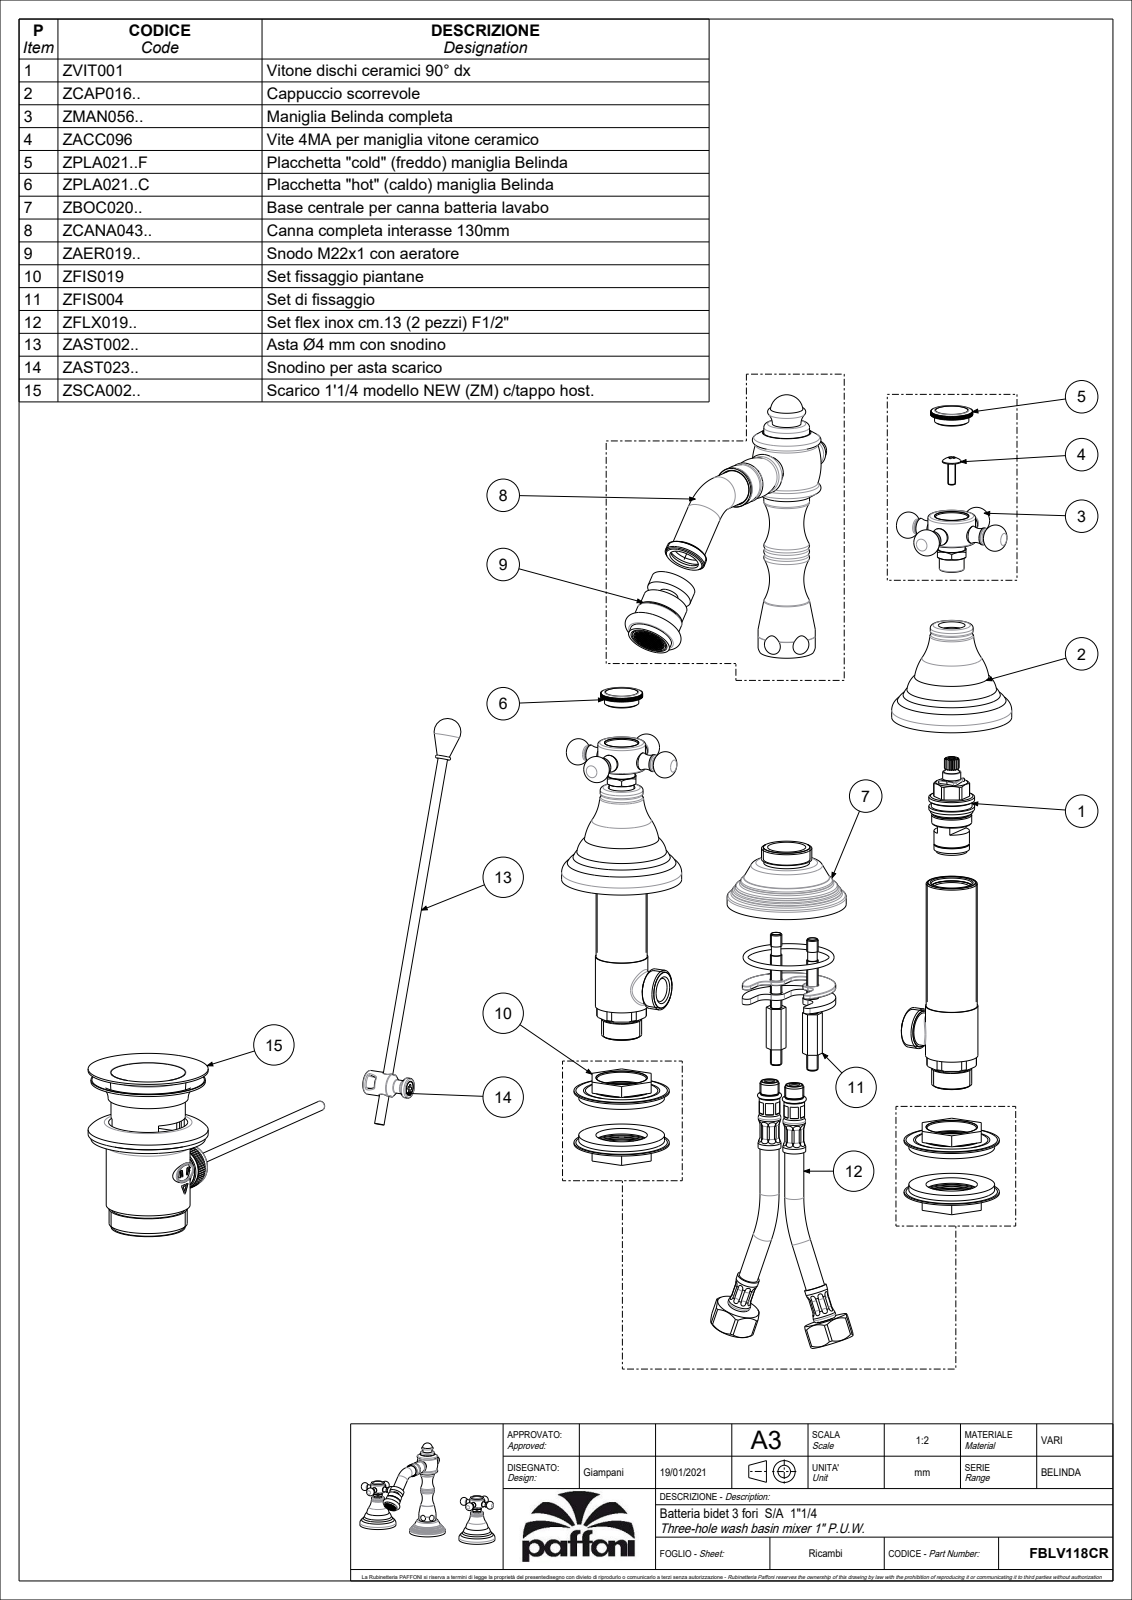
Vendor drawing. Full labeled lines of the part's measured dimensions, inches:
Part name (STEP PRODUCT): FBLV118CR
STEP written by: CREO PARAMETRIC BY PTC INC, 2020044 (CONFIG_CONTROL_DESIGN)
Units: inches
Bodies: 5 solids, 1127 faces (467 planar, 332 cylindrical, 328 other)
Overall size (bounding box): 10.396 × 8.047 × 7.042
Volume: 20.63 in³ · Surface area: 116.8 in²
Round holes (diameter × count): ⌀0.197 ×2, ⌀0.217 ×2, ⌀0.354 ×2, ⌀0.394 ×2, ⌀0.433 ×2, ⌀0.787 ×1, ⌀0.949 ×1, ⌀1.909 ×1
Round bosses / shafts (diameter × count): ⌀0.984 ×3, ⌀0.354 ×3, ⌀0.276 ×3, ⌀2.48 ×2, ⌀0.945 ×2, ⌀0.886 ×2, ⌀0.709 ×2, ⌀0.551 ×2
Partial cylindrical surfaces — rounded edges, fillets, slot ends (radius × count): R0.433 ×2
Main face-to-face distances: 1.181, 2.378, 0.197, 0.079, 2.299, 1.118, 1.26, 0.709, 1.15, 0.953
Hole centre spacings: 0.355, 0.53, 0.535, 0.89, 0.591, 0.866
